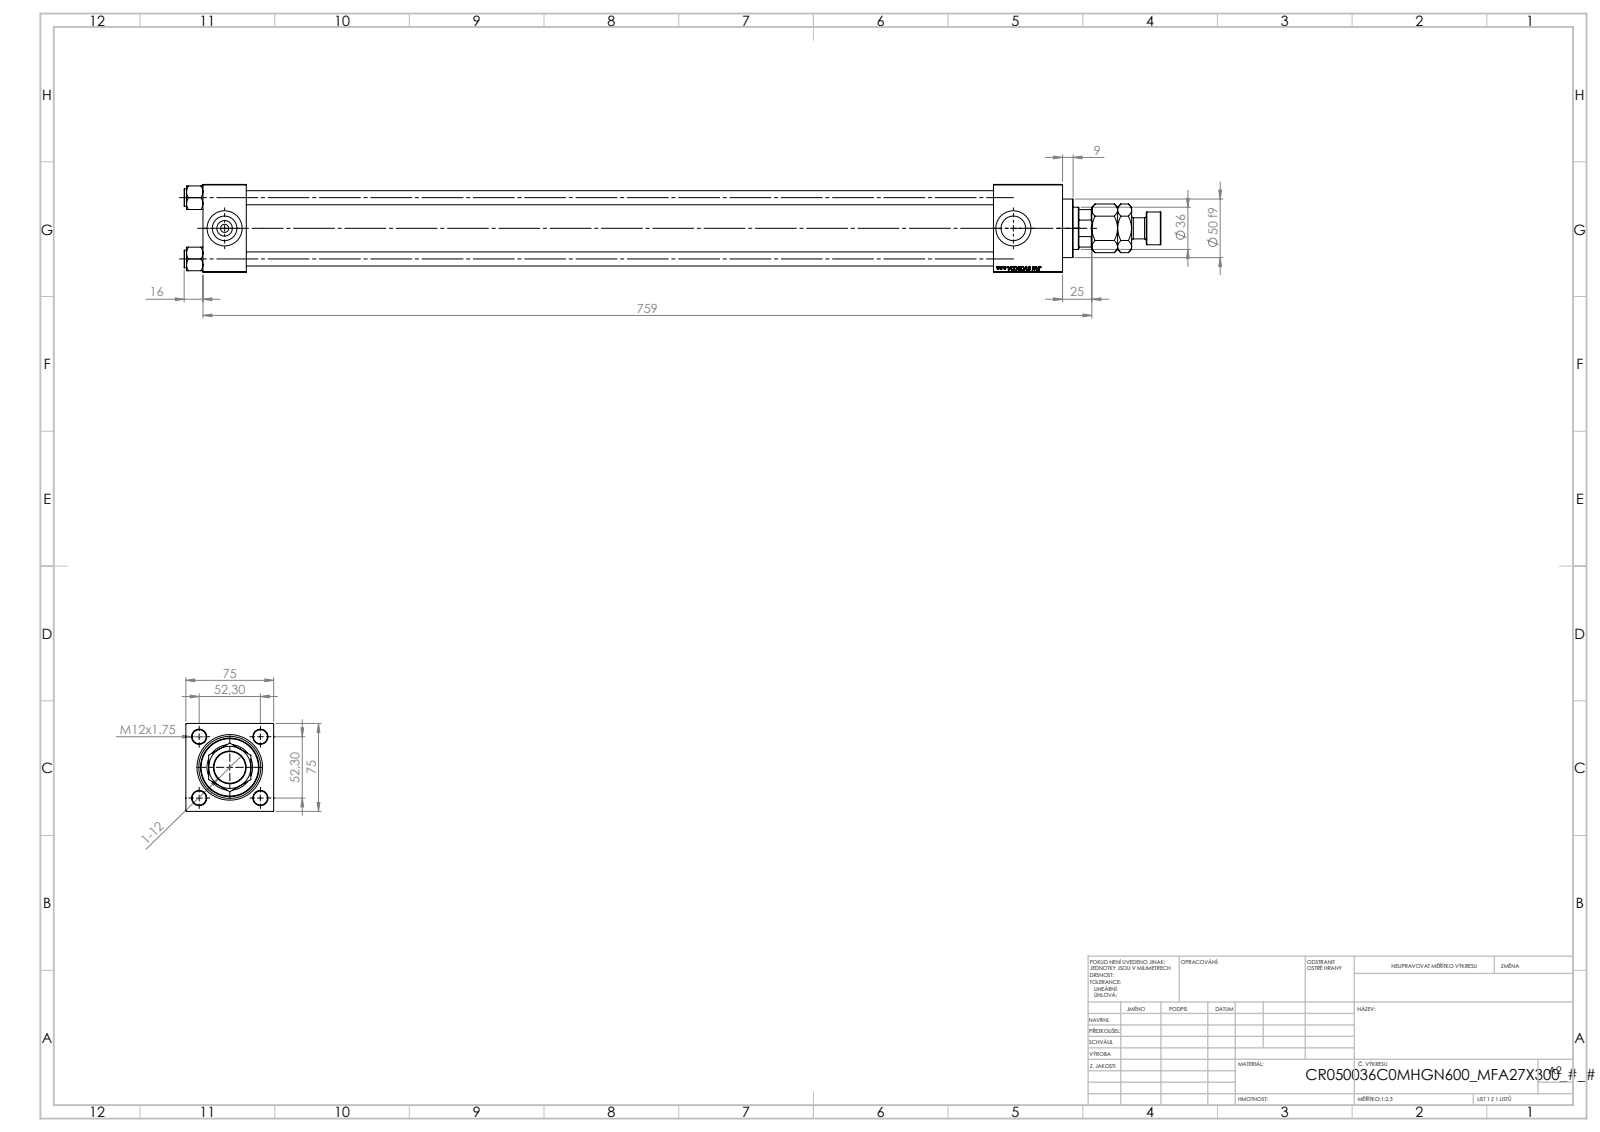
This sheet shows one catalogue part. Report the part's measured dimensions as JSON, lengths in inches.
{"part_name": "V215CR_VCP_C; V215CR_C_TYCINKA; NUT_M5_C; V215CR_C_Body (+2 more)", "step_written_by": "SolidWorks 2019 (CONFIG_CONTROL_DESIGN)", "units": "inches", "bodies": {"solids": 12, "faces": 1206, "planar": 544, "cylindrical": 94, "other": 568}, "overall_size": [32.835, 2.974, 2.953], "volume_in3": 114.5, "surface_area_in2": 791.4, "round_holes": [[0.472, 4], [0.098, 2], [0.276, 2], [0.825, 2], [1.181, 2], [1.004, 1], [1.417, 1], [1.535, 1], [1.614, 1], [2.087, 1]], "round_bosses_or_shafts": [[0.591, 4], [2.205, 1], [1.969, 1], [1.102, 1], [0.709, 1]], "partial_cylinders_radius": [[0.689, 1]], "face_to_face_distances": [2.953, 1.457, 2.323, 26.575, 25.118, 28.898, 27.441, 3.307, 0.984, 27.768], "hole_center_spacings": [1.031, 1.456, 2.059, 2.253, 0.974, 2.912, 1.949, 26.516]}
